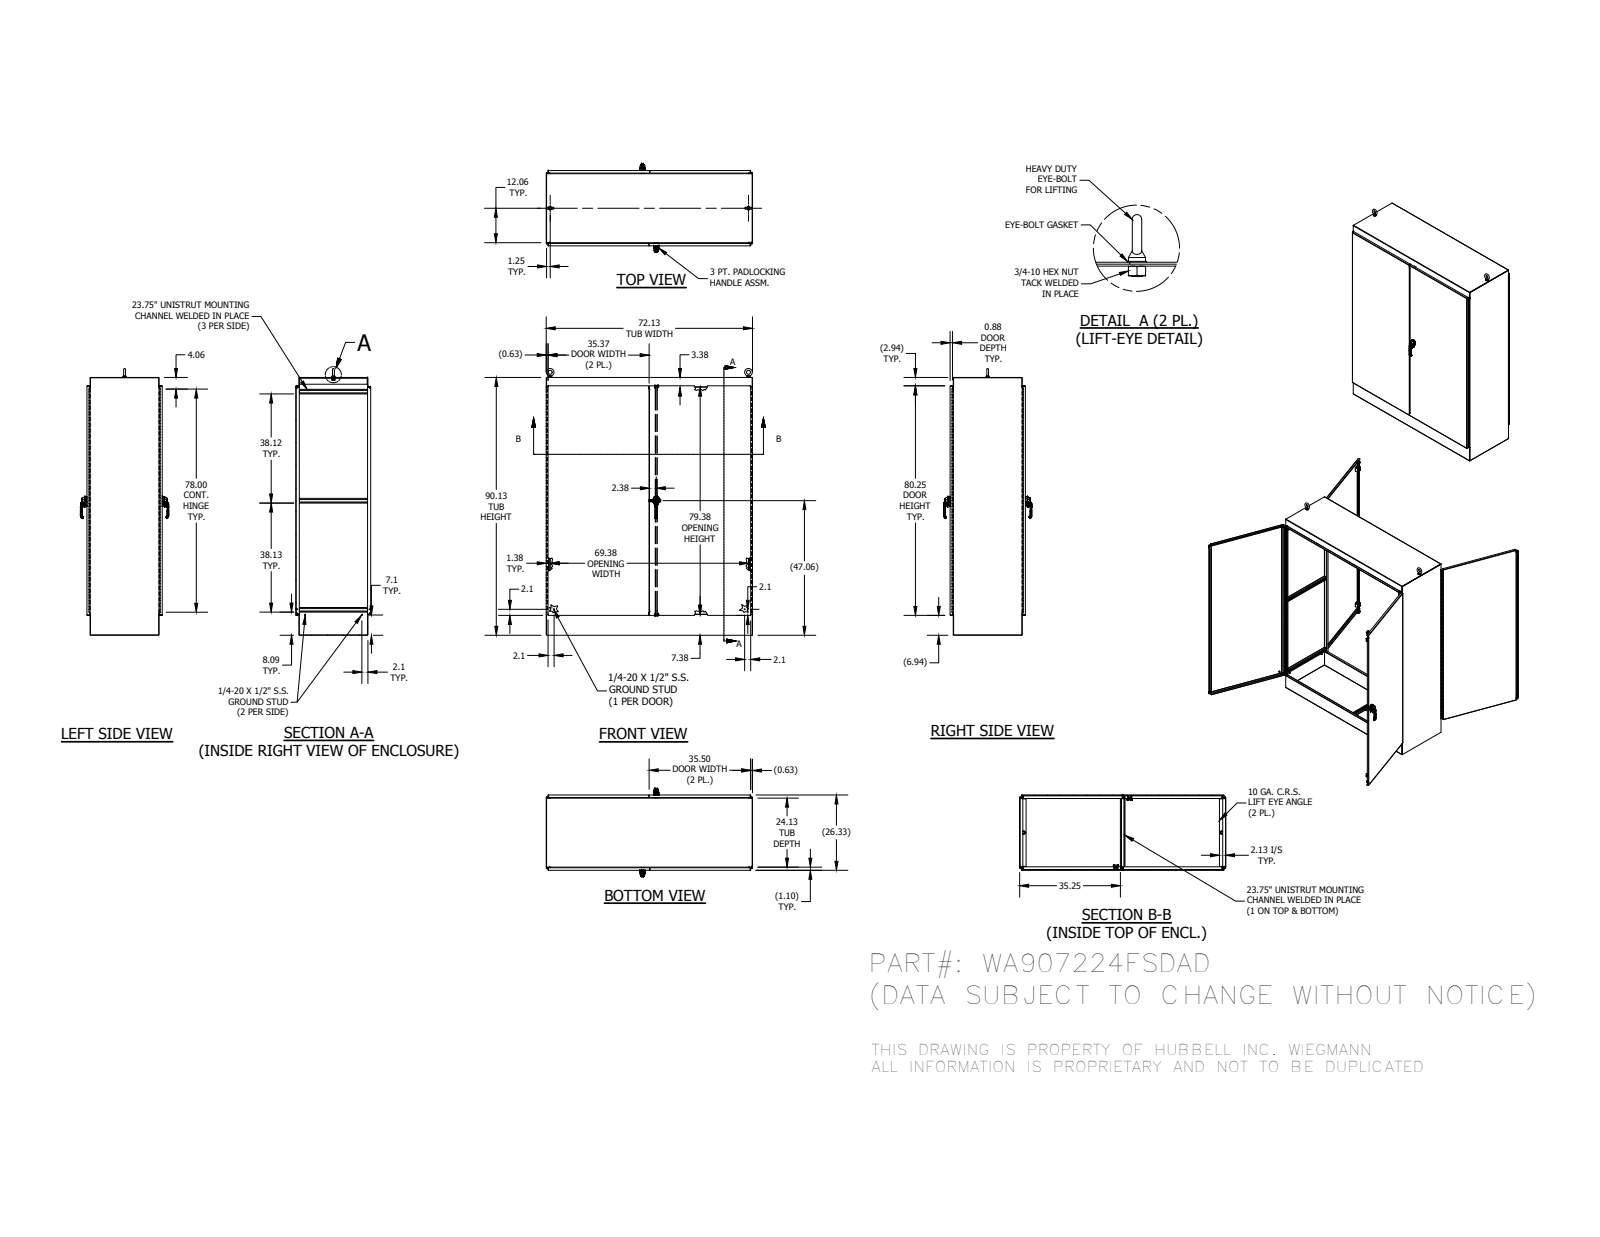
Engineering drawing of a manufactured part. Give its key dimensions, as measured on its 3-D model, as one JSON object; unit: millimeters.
{"part_name": "FUN00103; HFW3025; 316298; 349132 (+8 more)", "step_written_by": "Autodesk Inventor 2014 (AUTOMOTIVE_DESIGN)", "units": "millimeters", "bodies": {"solids": 110, "faces": 7168, "planar": 3386, "cylindrical": 2398, "other": 1384}, "overall_size": [2368.49, 1832.09, 784.13], "volume_mm3": 51840000, "surface_area_mm2": 33130000, "round_holes": [[9.52, 32], [7.02, 16], [5.08, 8], [5.4, 6], [6, 6], [7.11, 6], [3.61, 4], [4.57, 4], [6.13, 4], [6.35, 4], [6.41, 4], [10.16, 4]], "round_bosses_or_shafts": [[25.4, 4], [14.29, 4], [13.37, 4], [12.7, 4], [9.52, 4], [8.56, 4], [8.38, 4], [7.94, 4]], "partial_cylinders_radius": [[0.5, 345], [0.3, 169], [0.79, 46], [3.97, 40], [0.47, 38], [0.25, 32], [2, 30], [3, 29]], "face_to_face_distances": [3.18, 3.17, 662.54, 665.71, 668.89, 665.72, 1828.8, 2286, 28.06, 637.66], "hole_center_spacings": [660.4, 220.13, 440.27, 1798.26, 1804.99, 1818.36, 1838.24, 1864.41]}
